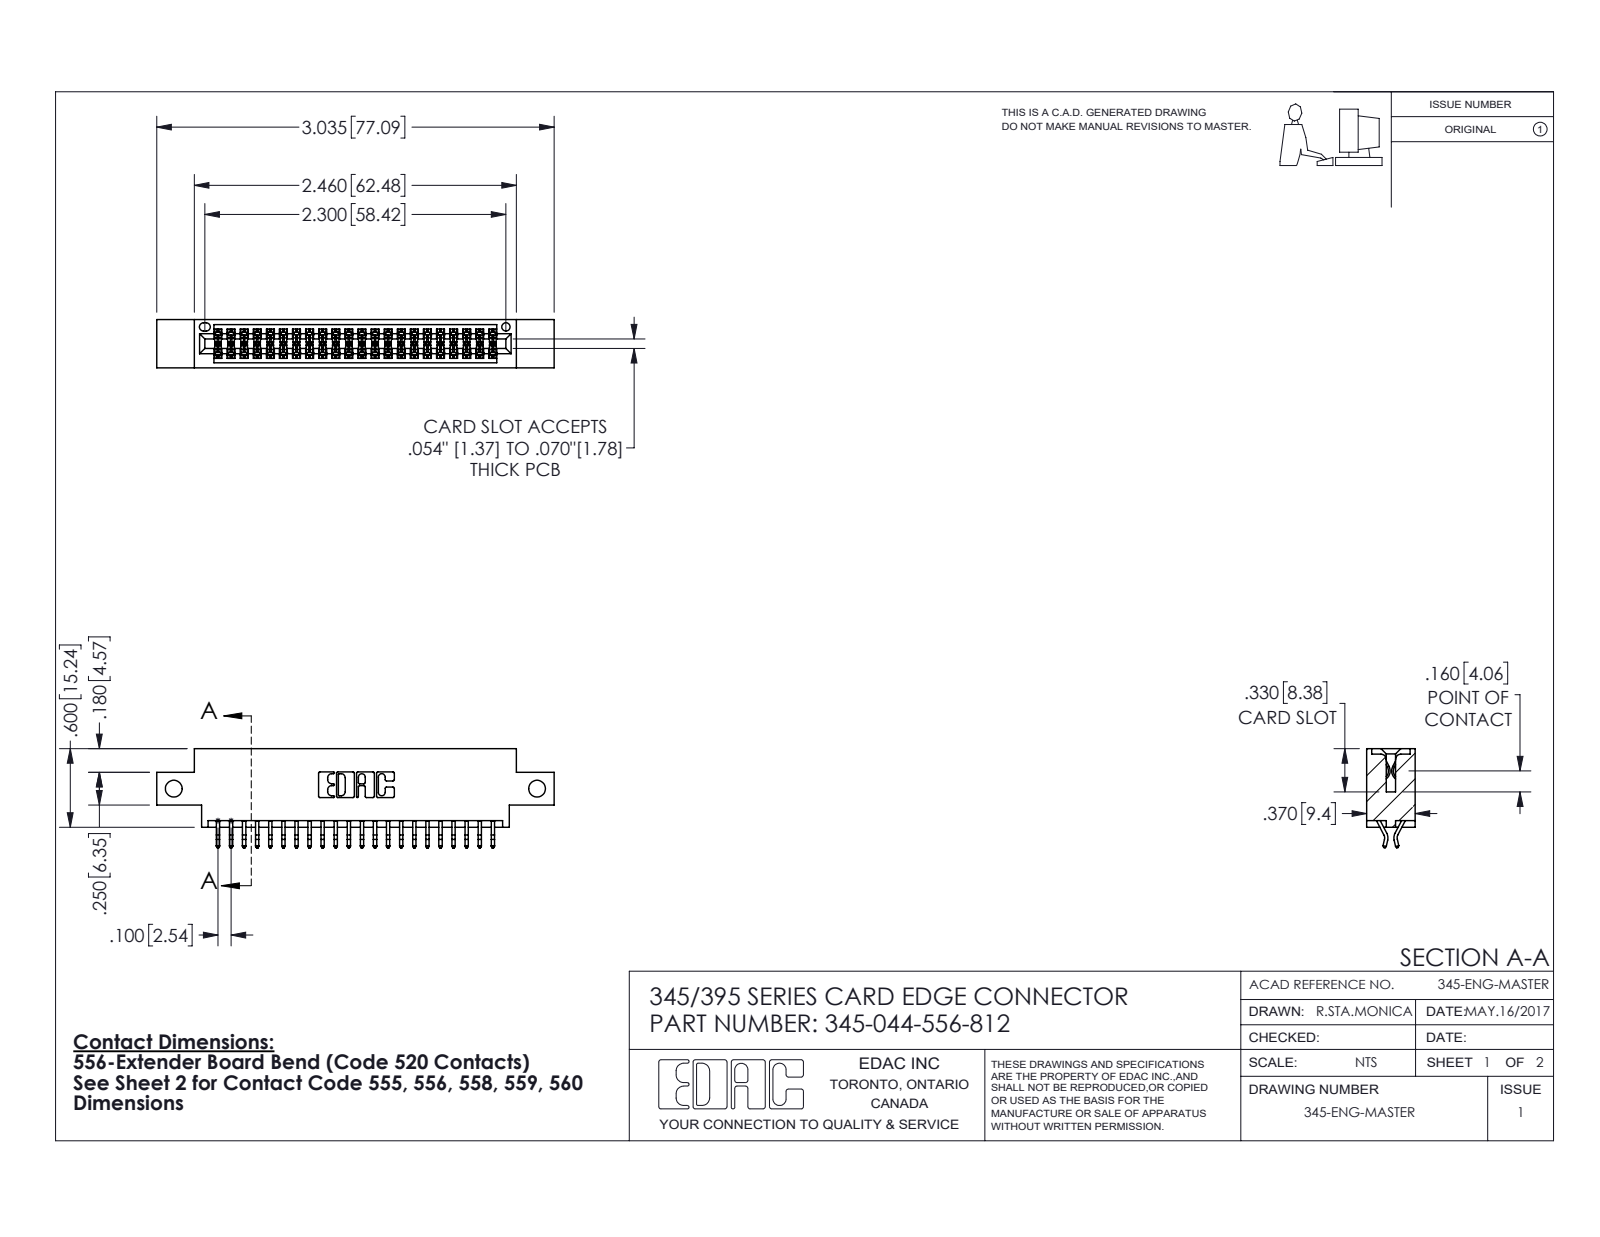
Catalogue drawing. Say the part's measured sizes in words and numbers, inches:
The part is named "345-044-556-812; 345-292-001_556 Tail; 345 Part_0.170 Offset - Side Mount". Its 3-D file was written by "SolidWorks 2016 (CONFIG_CONTROL_DESIGN)". It is 45 solids with 2594 faces: 1712 planar, 882 cylindrical and 0 other. Overall it measures 3.035 by 0.757 by 0.37 inches. Its volume is 0.433 cubic inches and its surface area 15.62 square inches. Round holes: 2 of diameter 0.128, 1 of diameter 0.064. Partial cylindrical surfaces (rounded edges, fillets, slot ends): 66 of radius 0.006, 22 of radius 0.01, 6 of radius 0.007, 6 of radius 0.031, 3 of radius 0.026, 2 of radius 0.01, 2 of radius 0.014, 2 of radius 0.019. The main face-to-face distances are 0.298, 0.072, 0.37, 0.2, 0.025, 0.098, 0.272, 0.225, 0.175, 0.15. The hole center spacings are 2.775.
